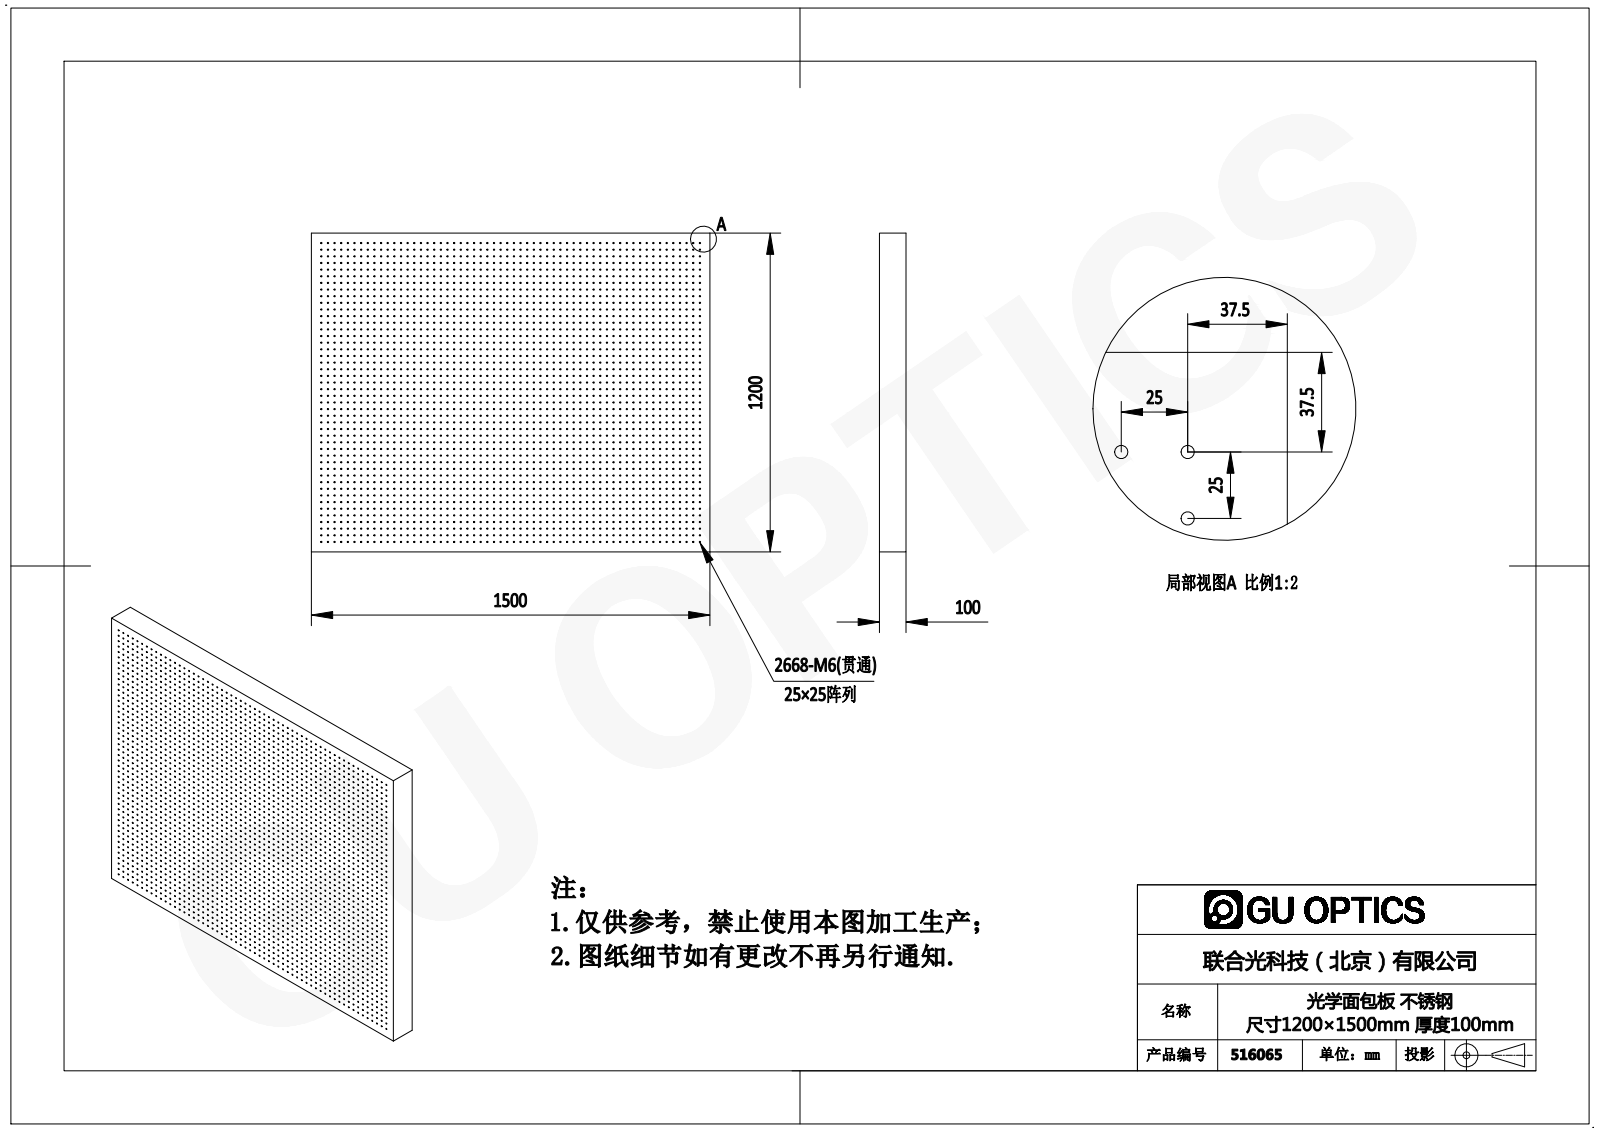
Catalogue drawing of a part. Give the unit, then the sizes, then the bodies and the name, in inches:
Units: inches
Overall size (bounding box): 59.055 × 47.244 × 3.937
Round holes (diameter × count): ⌀0.197 ×2668
Main face-to-face distances: 3.937, 47.244, 59.055
Hole centre spacings: 0.984, 1.969, 2.953, 3.937, 4.921, 5.906, 6.89, 7.874
Volume: 10 670 in³ · Surface area: 12 750 in²
Bodies: 1 solid, 5342 faces (6 planar, 5336 cylindrical, 0 other)
Part name (STEP PRODUCT): 516065
STEP written by: SolidWorks 2016 (AUTOMOTIVE_DESIGN)
